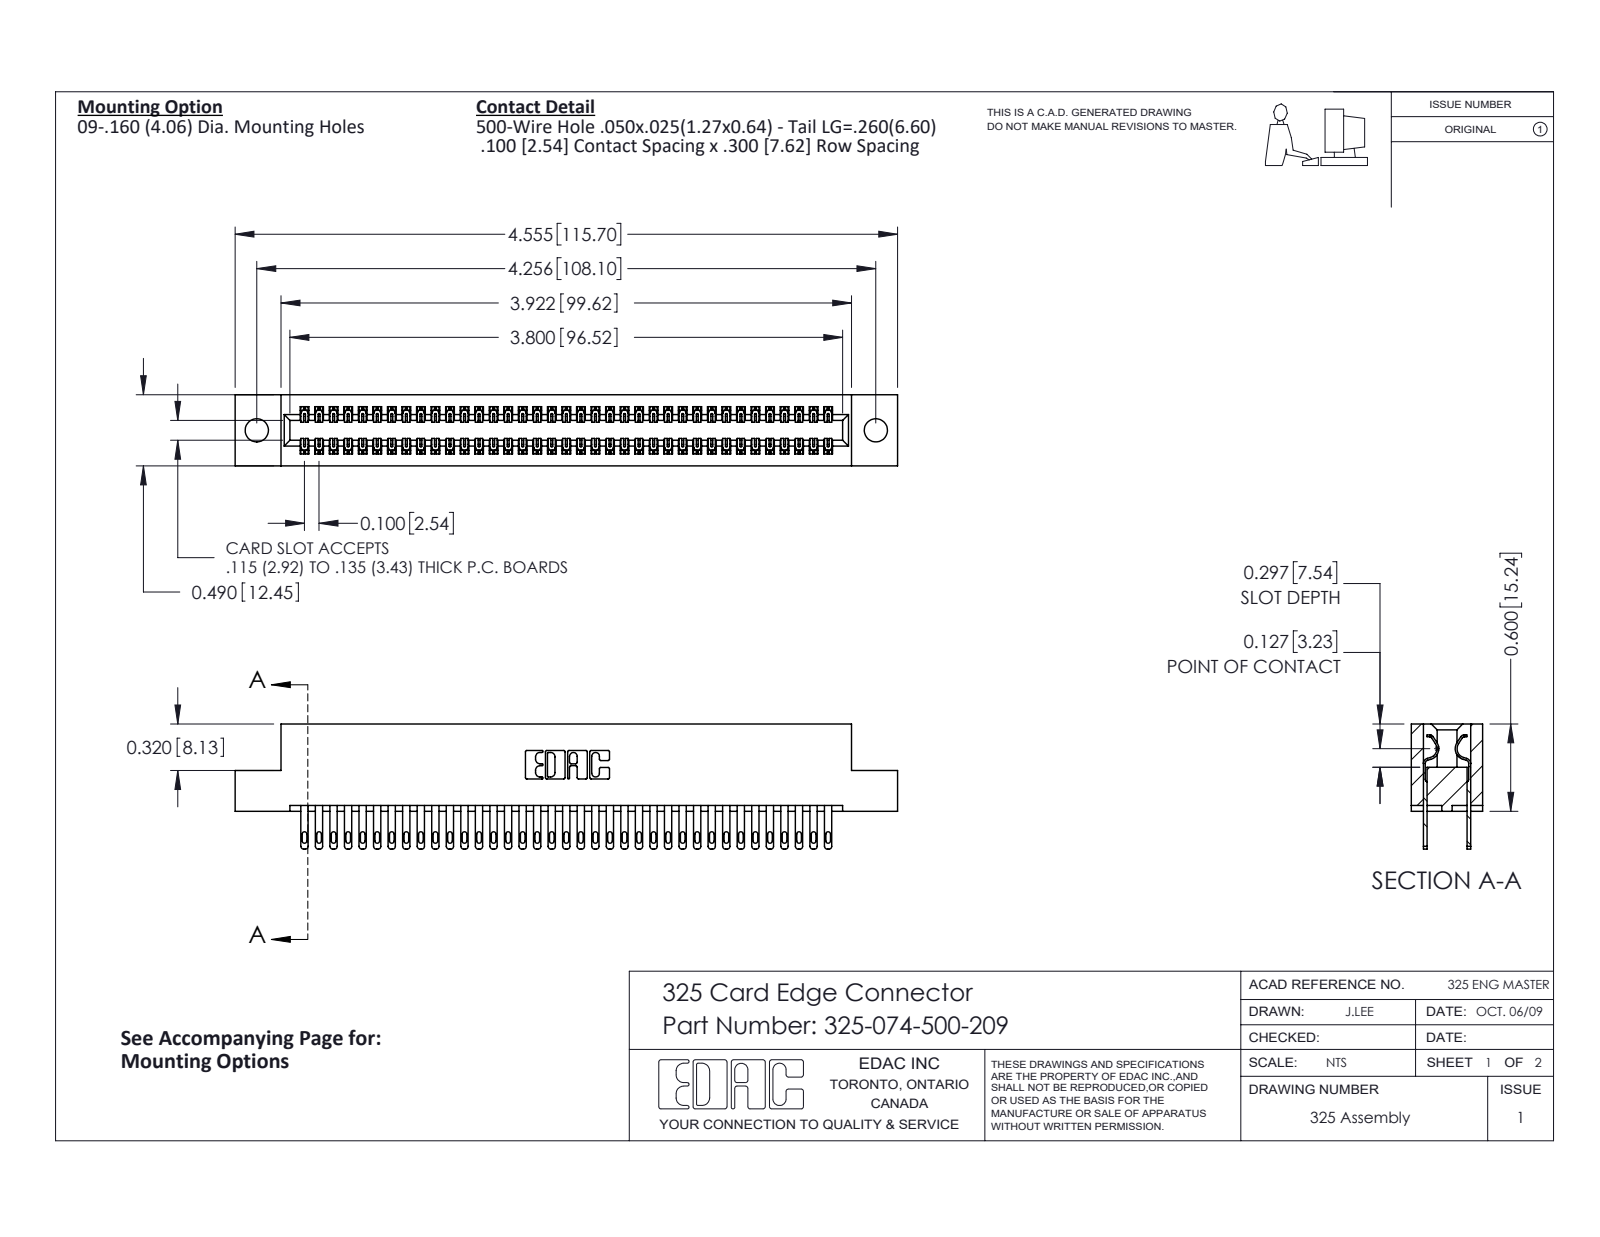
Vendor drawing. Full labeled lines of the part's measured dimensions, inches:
Part name (STEP PRODUCT): 325 Part_.160 TH; 325-074-500-209; 325-292-001_325-293-100
STEP written by: SolidWorks 2016 (CONFIG_CONTROL_DESIGN)
Units: inches
Bodies: 75 solids, 3666 faces (2290 planar, 1376 cylindrical, 0 other)
Overall size (bounding box): 4.555 × 0.86 × 0.49
Volume: 0.908 in³ · Surface area: 28.82 in²
Round holes (diameter × count): ⌀0.16 ×2
Partial cylindrical surfaces — rounded edges, fillets, slot ends (radius × count): R0.006 ×111, R0.016 ×74, R0.02 ×74, R0.01 ×22, R0.007 ×6, R0.031 ×6, R0.026 ×3, R0.014 ×2
Main face-to-face distances: 0.083, 0.407, 0.3, 0.107, 0.383, 0.025, 0.49, 0.325, 0.275, 0.56
Hole centre spacings: 4.256
